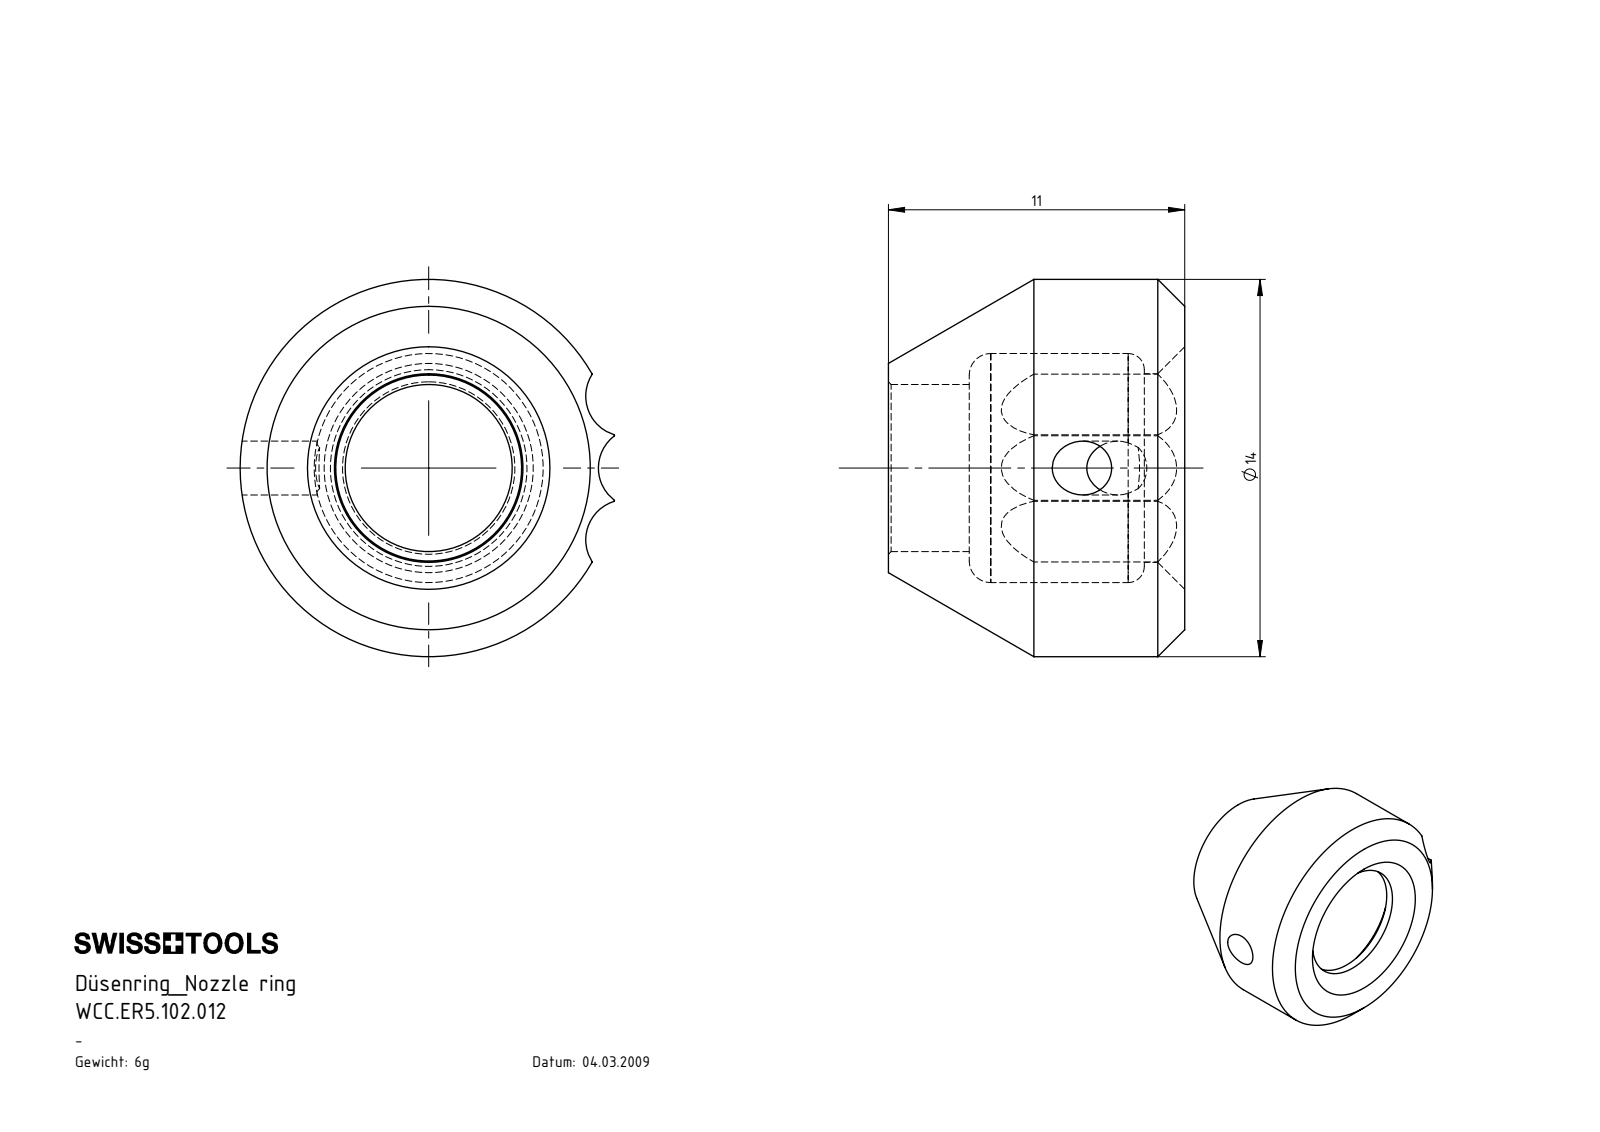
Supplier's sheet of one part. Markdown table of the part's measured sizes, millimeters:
| quantity | value |
| --- | --- |
| part name | WCC.ER5.102.012 |
| STEP written by | SolidWorks 2017 (AUTOMOTIVE_DESIGN) |
| units | millimeters |
| bodies | 1 solid, 21 faces (5 planar, 10 cylindrical, 6 other) |
| overall size | 14 × 13.9 × 11 |
| volume | 805 mm³ |
| surface area | 862 mm² |
| round holes (diameter × count) | 2 × 1, 6.2 × 1, 7 × 1, 8.5 × 1 |
| round bosses / shafts (diameter × count) | 14 × 1 |
| partial cylindrical surfaces (radius × count) | 1.5 × 3 |
| main face-to-face distances | 11, 3, 8, 9.5, 6.5, 1.5 |
